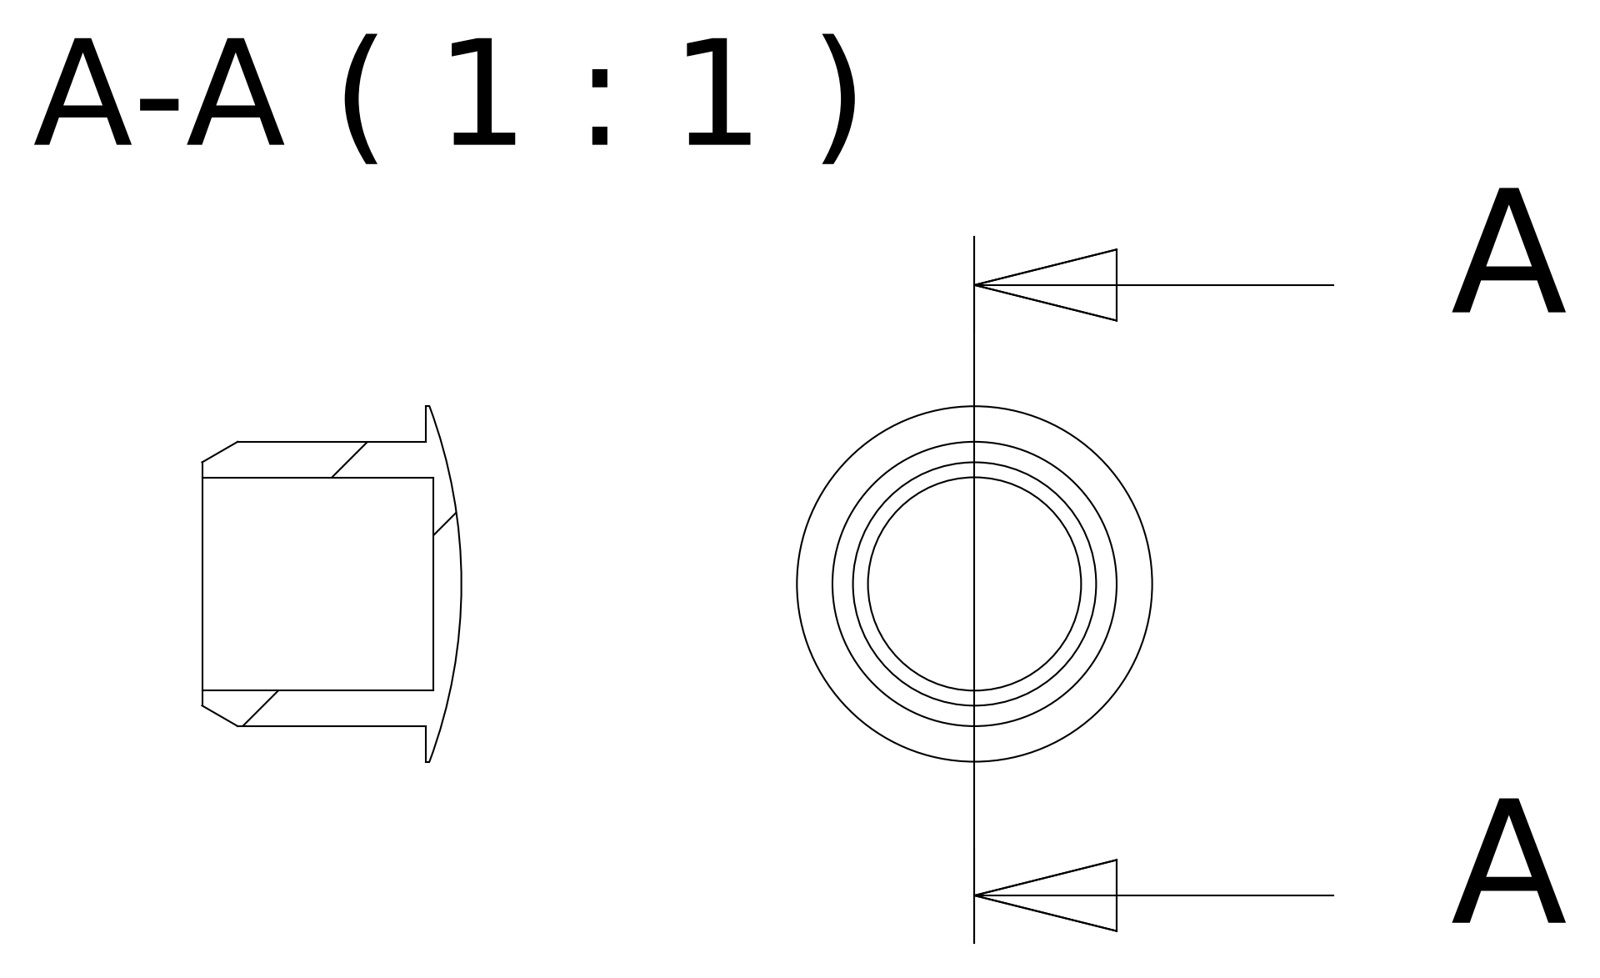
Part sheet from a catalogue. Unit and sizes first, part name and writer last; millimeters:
Units: millimetres
Overall size (bounding box): 10 × 10 × 7.3
Round holes (diameter × count): ⌀6 ×1
Round bosses / shafts (diameter × count): ⌀10 ×1, ⌀8 ×1
Main face-to-face distances: 6.3, 6.5
Volume: 170 mm³ · Surface area: 432 mm²
Bodies: 1 solid, 8 faces (3 planar, 3 cylindrical, 2 other)
Part name (STEP PRODUCT): CTPTF0000012
STEP written by: Autodesk Inventor 2016 (AUTOMOTIVE_DESIGN)
